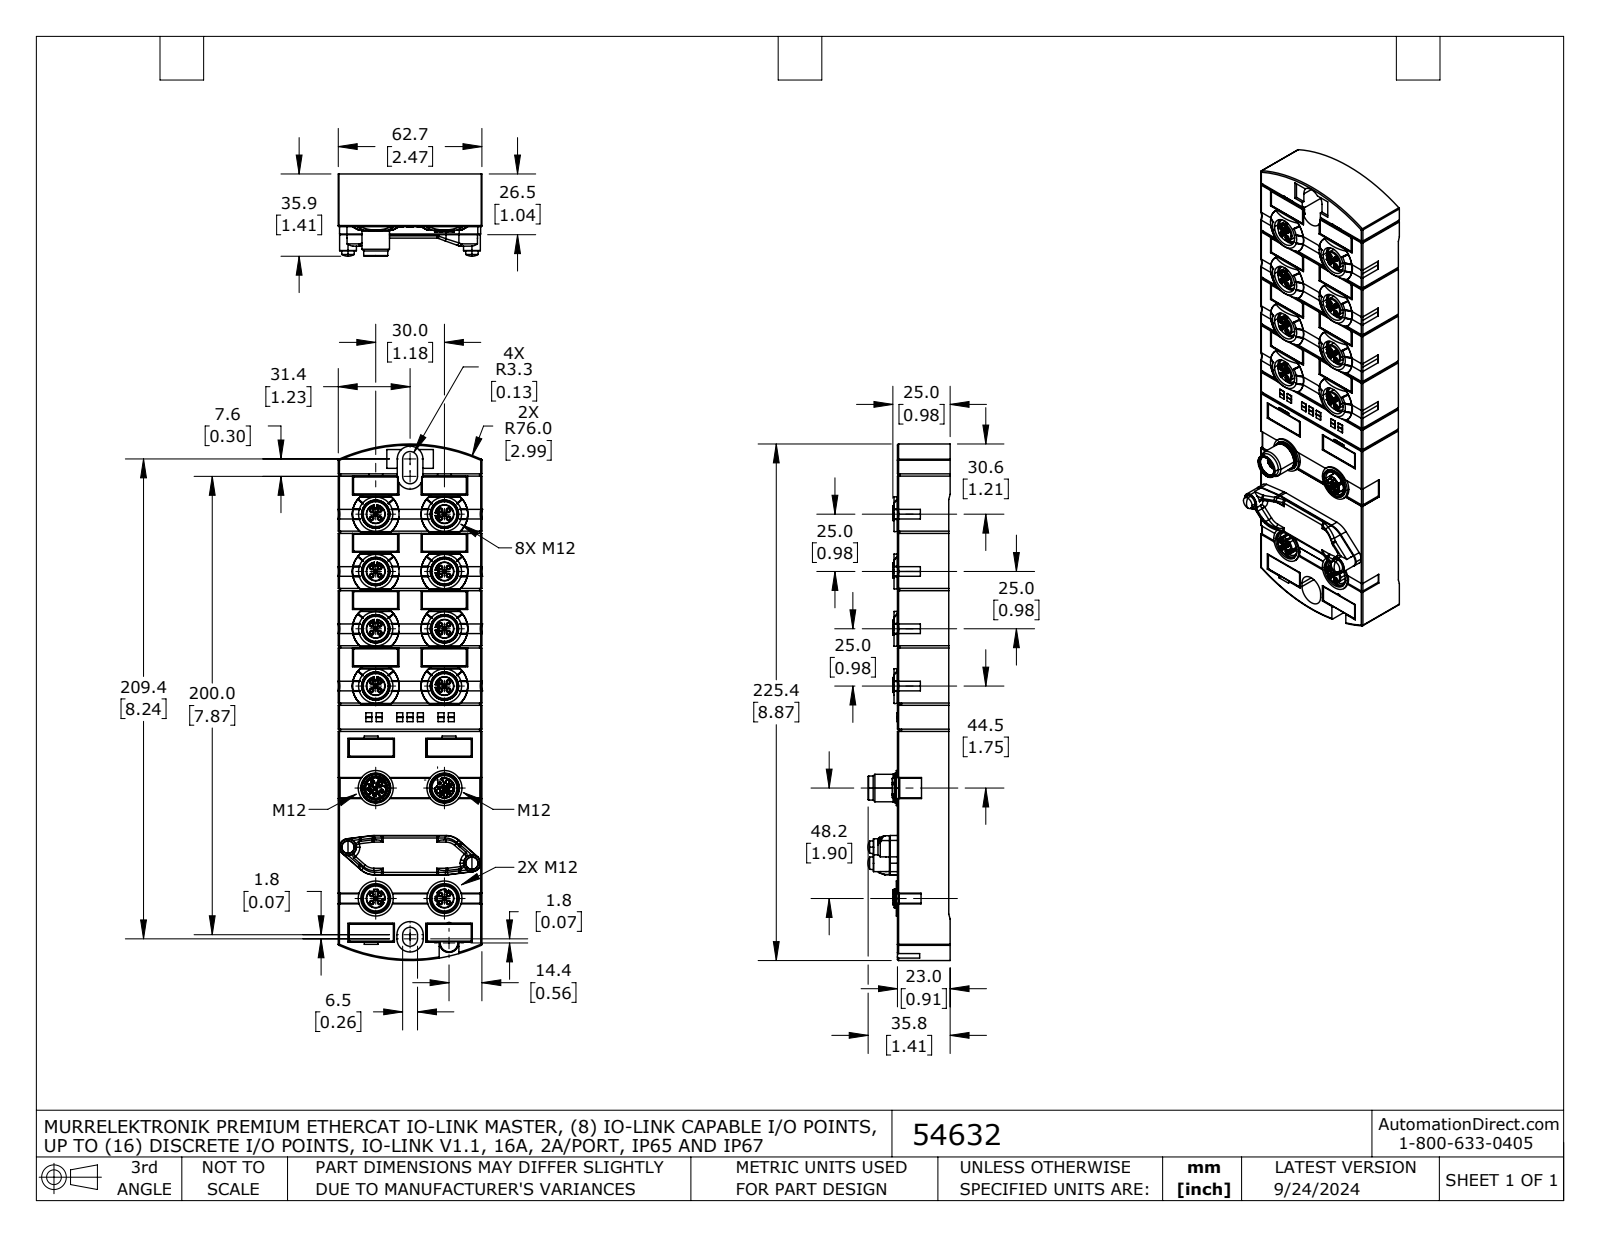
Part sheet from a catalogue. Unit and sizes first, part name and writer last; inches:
Units: inches
Overall size (bounding box): 8.874 × 2.469 × 1.413
Round holes (diameter × count): ⌀0.047 ×50, ⌀0.43 ×9, ⌀0.061 ×4, ⌀0.065 ×4, ⌀0.43 ×2, ⌀0.512 ×2, ⌀0.128 ×1, ⌀0.161 ×1, ⌀0.35 ×1
Round bosses / shafts (diameter × count): ⌀0.079 ×50, ⌀0.323 ×10, ⌀0.059 ×5, ⌀0.602 ×4, ⌀0.516 ×2, ⌀0.289 ×2, ⌀0.484 ×1, ⌀0.472 ×1
Partial cylindrical surfaces — rounded edges, fillets, slot ends (radius × count): R0.02 ×64, R0.039 ×21, R0.01 ×20, R0.008 ×15, R0.006 ×14, R0.004 ×13, R0.394 ×12, R0.012 ×10
Main face-to-face distances: 0.882, 2.469, 0.024, 0.906, 0.904, 0.88, 0.02, 0.217, 0.059, 0.199
Hole centre spacings: 0.098, 0.139, 0.197, 0.984, 0.917, 0.994, 1.056, 1.181
Volume: 18.87 in³ · Surface area: 85.67 in²
Bodies: 6 solids, 2128 faces (771 planar, 677 cylindrical, 680 other)
Part name (STEP PRODUCT): 54632
STEP written by: SolidWorks 2021 (AUTOMOTIVE_DESIGN)
